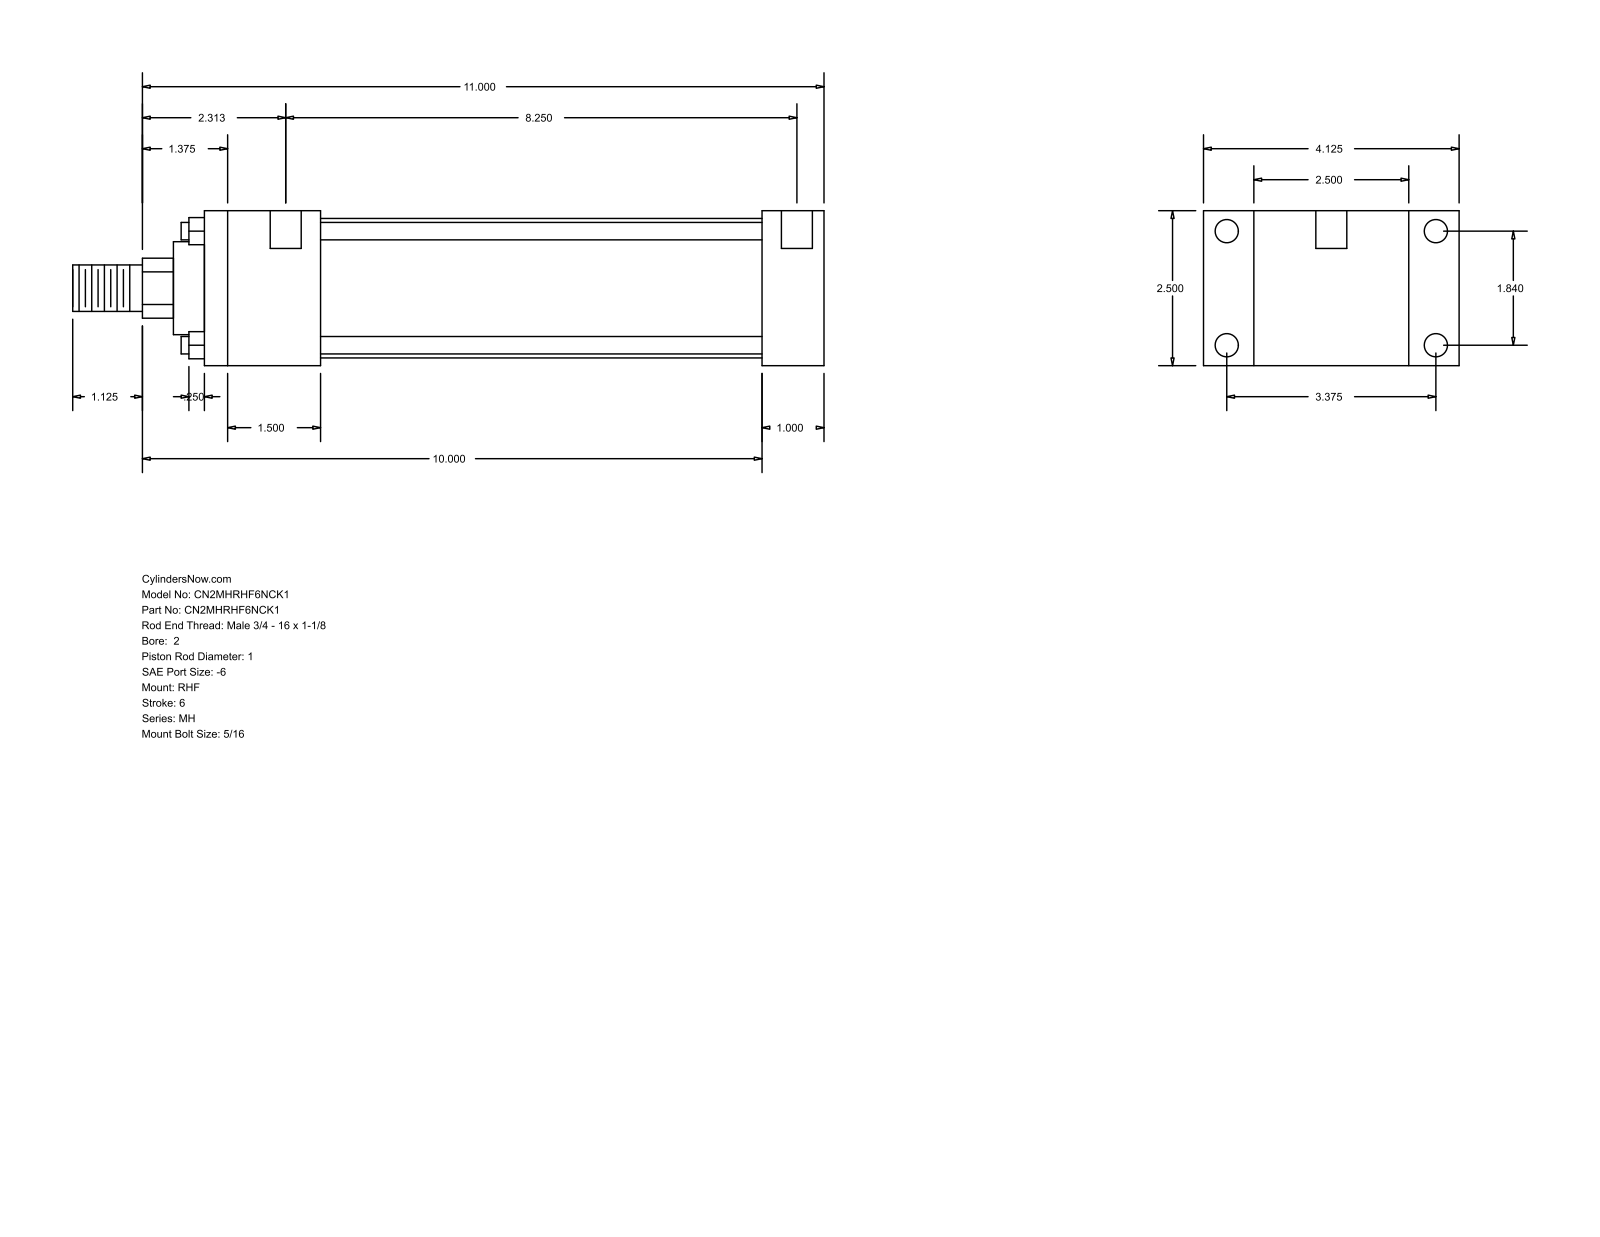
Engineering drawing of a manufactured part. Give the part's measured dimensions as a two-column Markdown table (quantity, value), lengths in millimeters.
| quantity | value |
| --- | --- |
| part name | MH_RHF__0200_1 |
| STEP written by | GSSL Pune (CONFIG_CONTROL_DESIGN) |
| units | millimeters |
| bodies | 0 solids, 88 faces (60 planar, 28 cylindrical, 0 other) |
| overall size | 307.98 × 104.78 × 63.5 |
| round holes (diameter × count) | 5.56 × 4, 9.53 × 4, 12.7 × 2 |
| round bosses / shafts (diameter × count) | 7.14 × 4, 57.15 × 1, 38.1 × 1, 25.4 × 1, 19.05 × 1 |
| partial cylindrical surfaces (radius × count) | 12.29 × 1 |
| main face-to-face distances | 63.5, 25.4, 20.64, 84.14, 254, 228.6, 104.78, 47.63, 180.97, 206.37 |
| hole center spacings | 46.74, 85.72, 97.63, 217.48, 3.17, 4.76, 209.55, 212.72 |
